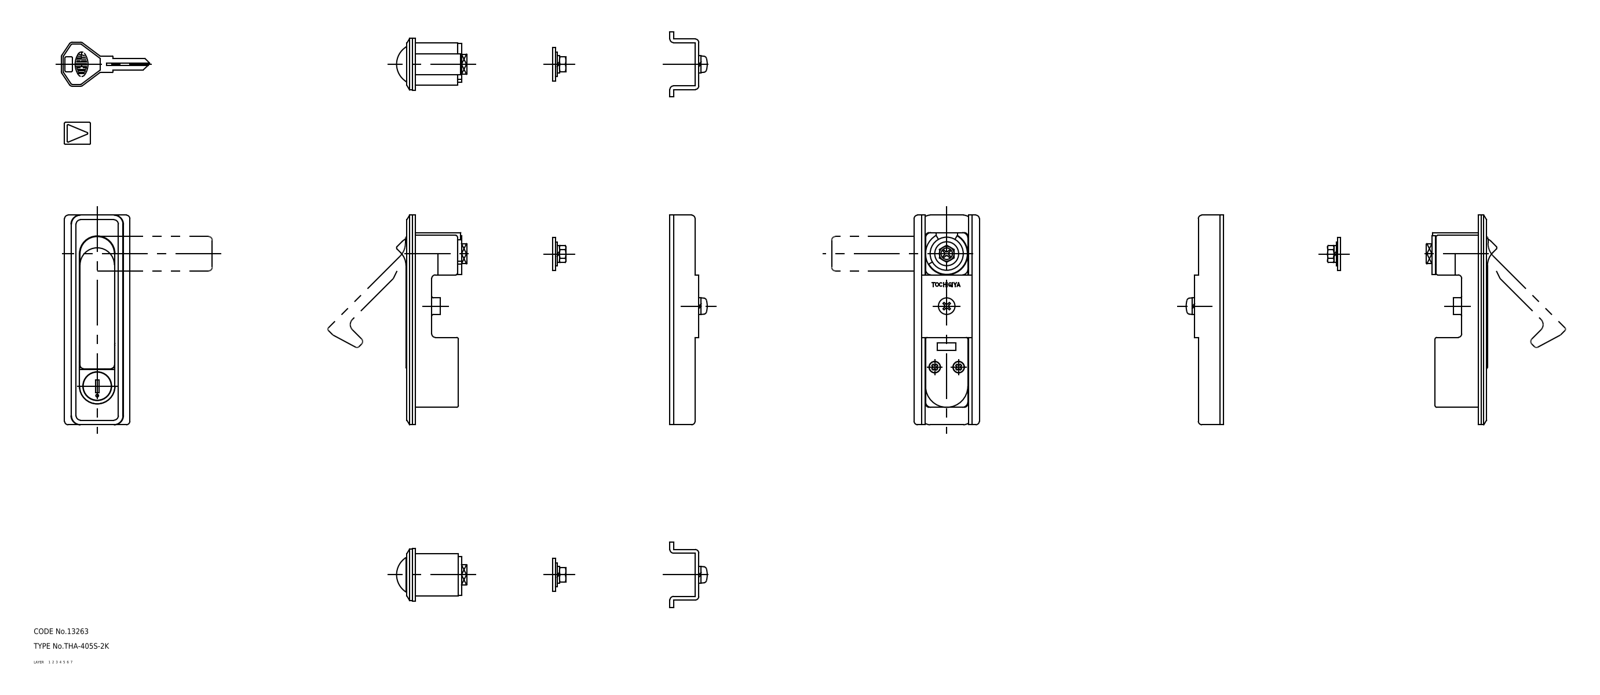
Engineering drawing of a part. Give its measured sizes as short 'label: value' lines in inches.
name: washer_B; washer_A; bolt; shaft (+8 more)
written by: CADfix (AUTOMOTIVE_DESIGN)
unit: in
bodies: 12 solids, 490 faces (0 planar, 0 cylindrical, 490 other)
size: 4.488 × 4.02 × 1.398
volume: 3.058 in³; area: 66.24 in²
